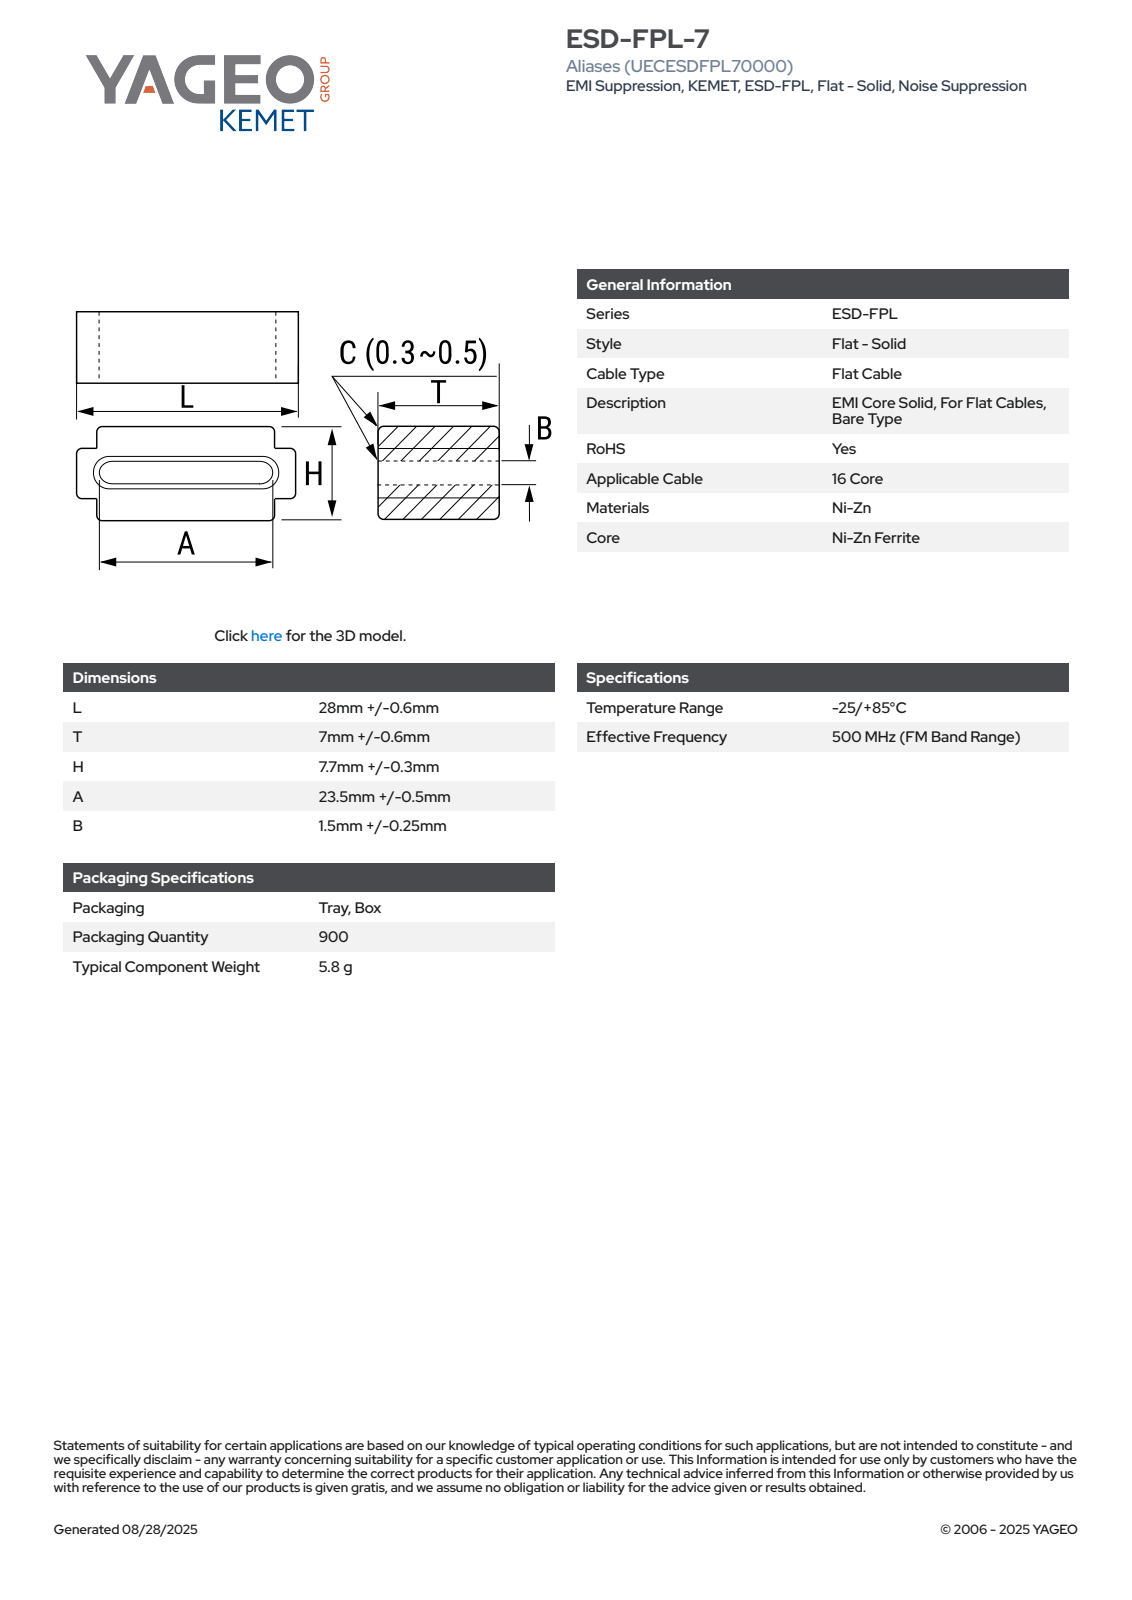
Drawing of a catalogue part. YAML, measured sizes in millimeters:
part_name: "EC_FPL2_L28.6T7.6H8A23.5B1.5"
step_written_by: "SolidWorks 2014 (AUTOMOTIVE_DESIGN)"
units: millimeters
bodies: {solids: 1, faces: 143, planar: 70, cylindrical: 43, other: 30}
overall_size: [28, 7.7, 7.6]
volume: 1224
surface_area: 1205
partial_cylinders:
  - {radius: 0.25, count: 28}
  - {radius: 0.15, count: 4}
  - {radius: 0.77, count: 2}
face_to_face_distances: [3.1, 4.6, 7.7, 1.5, 7.6, 2.2, 5.5, 0.9, 2.4, 25.8]
